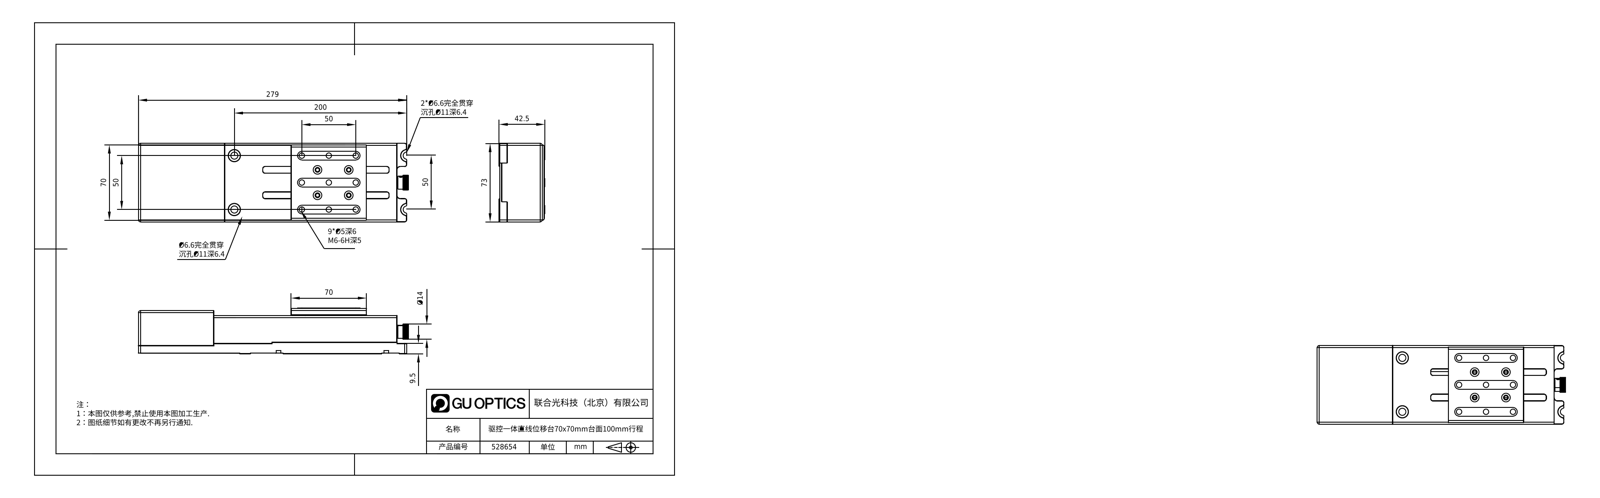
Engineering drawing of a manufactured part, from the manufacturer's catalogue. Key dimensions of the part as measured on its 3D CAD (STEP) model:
Part name (STEP PRODUCT): 528654
STEP written by: SolidWorks 2020 (CONFIG_CONTROL_DESIGN)
Units: millimetres
Bodies: 45 solids, 2403 faces (1245 planar, 756 cylindrical, 402 other)
Overall size (bounding box): 280.5 × 73 × 42.5
Volume: 481 117 mm³ · Surface area: 209 120 mm²
Round holes (diameter × count): ⌀2.4 ×46, ⌀1.6 ×26, ⌀4.4 ×25, ⌀4.2 ×22, ⌀2.5 ×17, ⌀1.57 ×16, ⌀3.4 ×16, ⌀6.5 ×12, ⌀5 ×10, ⌀3.3 ×6, ⌀1.57 ×4, ⌀2 ×4
Round bosses / shafts (diameter × count): ⌀2.2 ×4, ⌀2 ×4, ⌀22 ×1, ⌀12 ×1
Partial cylindrical surfaces — rounded edges, fillets, slot ends (radius × count): R2 ×31, R1 ×25, R4 ×6, R0.7 ×4, R1.3 ×4, R0.3 ×2, R0.4 ×2, R3 ×2
Main face-to-face distances: 2, 4, 1, 33, 35, 25, 26, 7, 2.5, 32.5
Hole centre spacings: 9, 18.26, 15, 30, 9.96, 9.97, 13.46, 15.59
